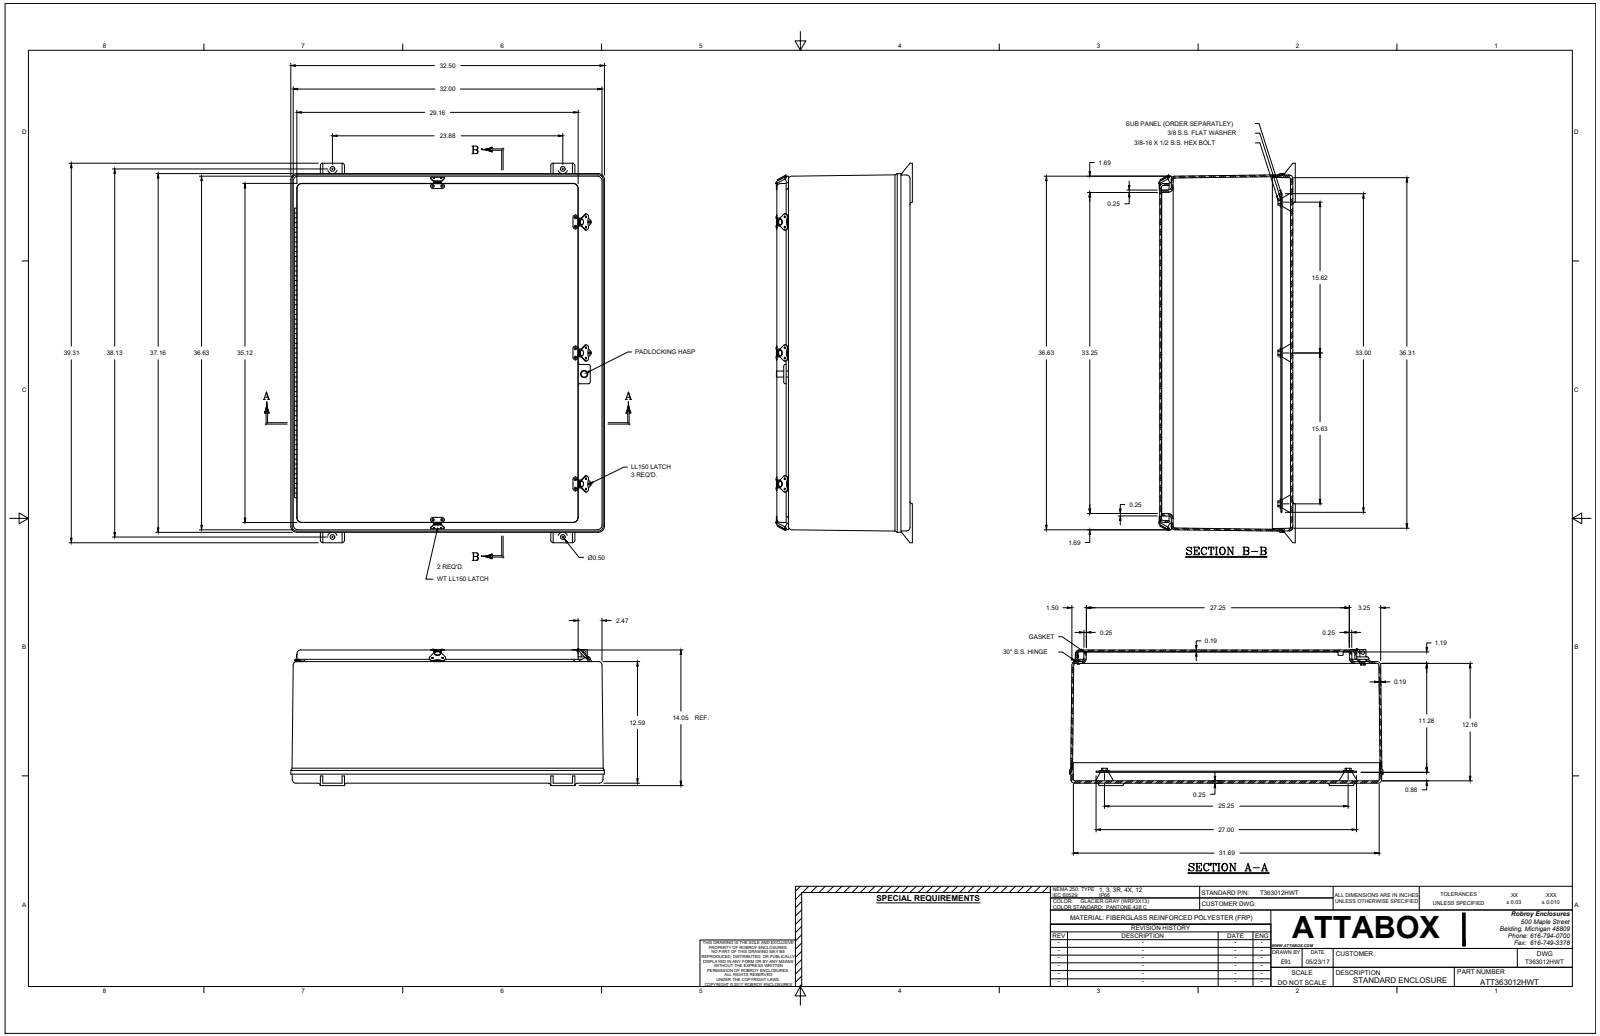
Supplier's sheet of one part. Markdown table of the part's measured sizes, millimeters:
| quantity | value |
| --- | --- |
| part name | T363012HWTL |
| STEP written by | SolidWorks 2018 (AUTOMOTIVE_DESIGN) |
| units | millimeters |
| bodies | 63 solids, 1821 faces (693 planar, 736 cylindrical, 392 other) |
| overall size | 998.6 × 825.5 × 365.7 |
| volume | 15 190 000 mm³ |
| surface area | 6 037 000 mm² |
| round holes (diameter × count) | 3.3 × 36, 1.6 × 20, 3.5 × 10, 4.7 × 10, 1.7 × 6, 14.3 × 4, 4 × 3, 1.7 × 2, 3.4 × 2, 11 × 2, 13 × 2, 13 × 2 |
| round bosses / shafts (diameter × count) | 3.6 × 20, 7.5 × 8, 12.7 × 5, 5.1 × 3, 3.4 × 2, 6.4 × 1, 5.1 × 1, 3.4 × 1 |
| partial cylindrical surfaces (radius × count) | 0.3 × 127, 6.4 × 24, 7.9 × 23, 0.8 × 20, 4.8 × 17, 9.5 × 13, 12.7 × 12, 3.2 × 10 |
| main face-to-face distances | 6.4, 4.8, 344.5, 350.9, 346, 339.7, 4.7, 4.8, 319.9, 31 |
| hole center spacings | 241.3, 495.3, 344.5, 25.4, 38.8, 254, 736.6, 88.2 |
